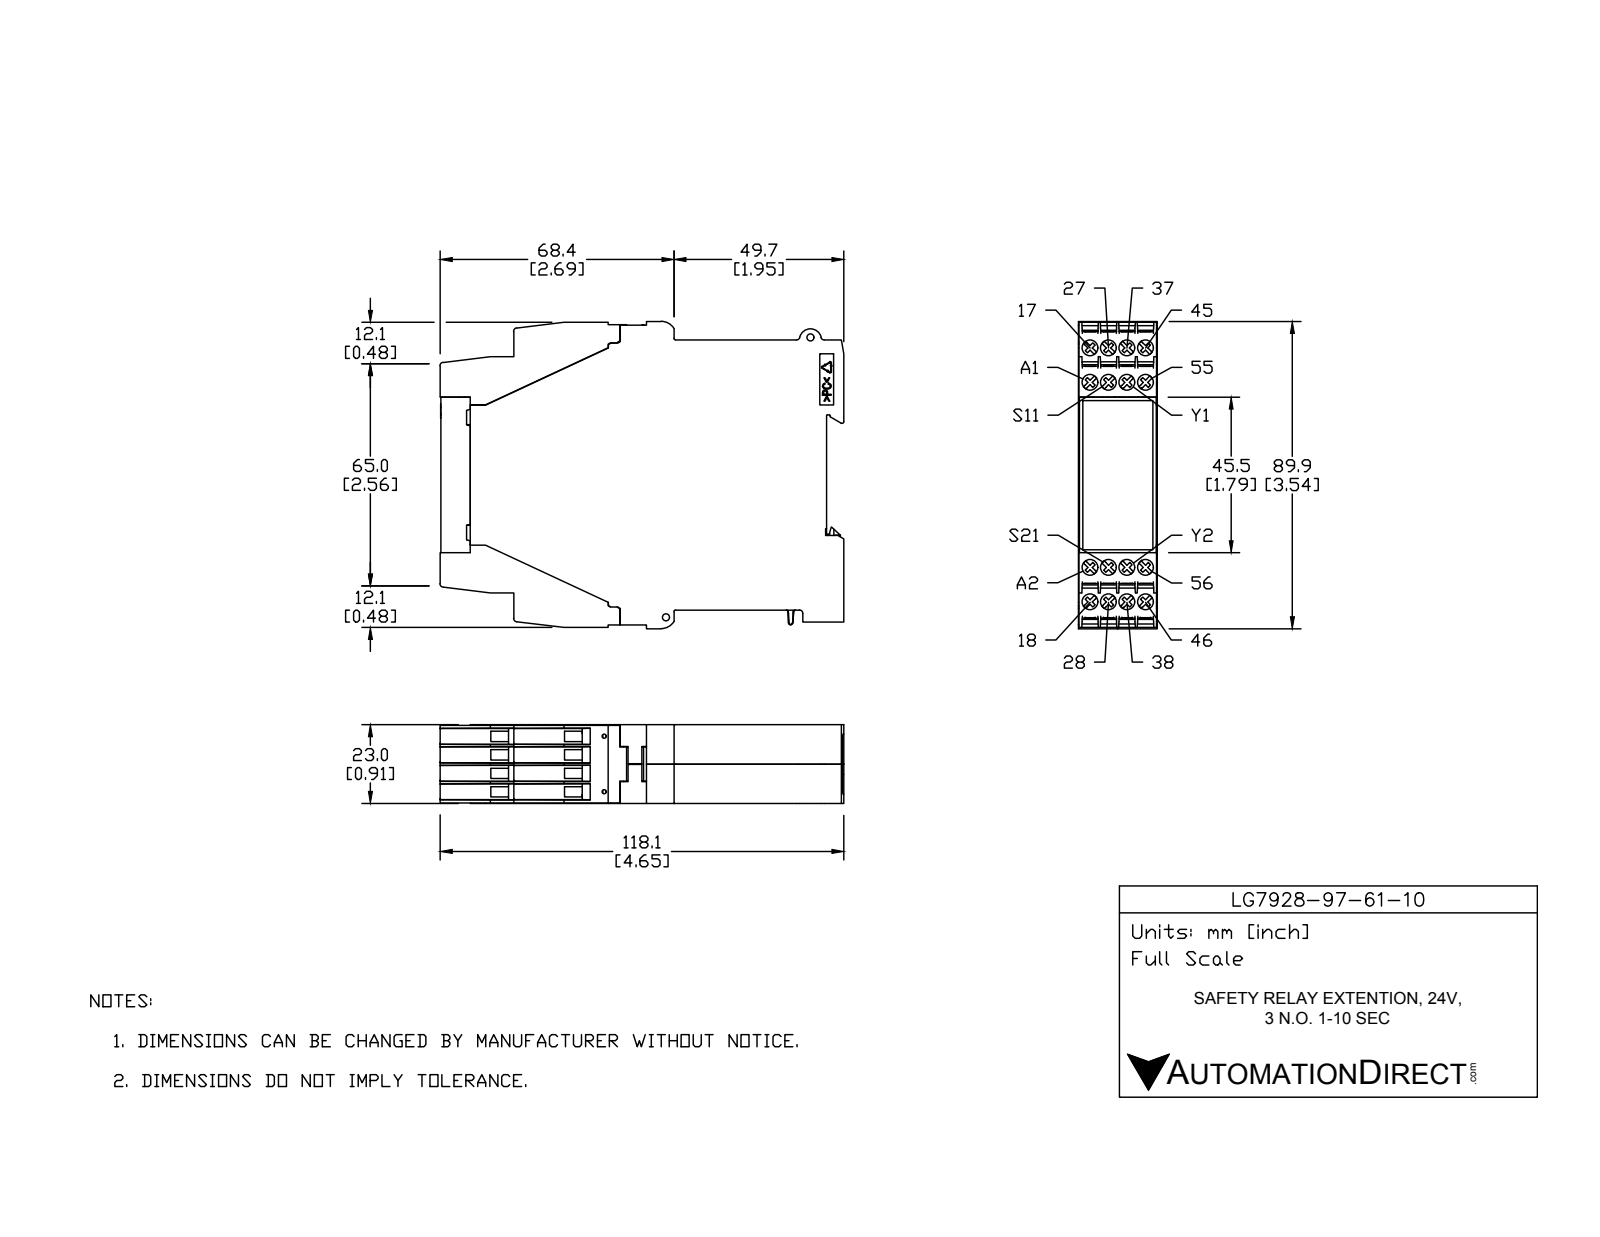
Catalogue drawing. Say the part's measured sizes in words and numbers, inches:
The part is named "LG7928-97-61-10". Its 3-D file was written by "SolidWorks 2017 (AUTOMOTIVE_DESIGN)". It is 1 solid with 2054 faces: 1604 planar, 319 cylindrical and 131 other. Overall it measures 4.656 by 3.537 by 0.906 inches. Its volume is 12.64 cubic inches and its surface area 62.74 square inches. Round holes: 16 of diameter 0.181, 3 of diameter 0.079, 2 of diameter 0.047, 2 of diameter 0.079. Round bosses or shafts: 16 of diameter 0.173, 1 of diameter 0.087. Partial cylindrical surfaces (rounded edges, fillets, slot ends): 52 of radius 0.008, 36 of radius 0.012, 31 of radius 0.02, 28 of radius 0.039, 6 of radius 0.006, 6 of radius 0.014, 2 of radius 0.174, 1 of radius 0.043. The main face-to-face distances are 0.906, 0.897, 0.894, 0.902, 4.451, 0.031, 0.874, 0.03, 0.039, 3.11. The hole center spacings are 0.213, 0.451, 2.541, 0.398, 0.425, 0.582, 2.531, 2.567.
